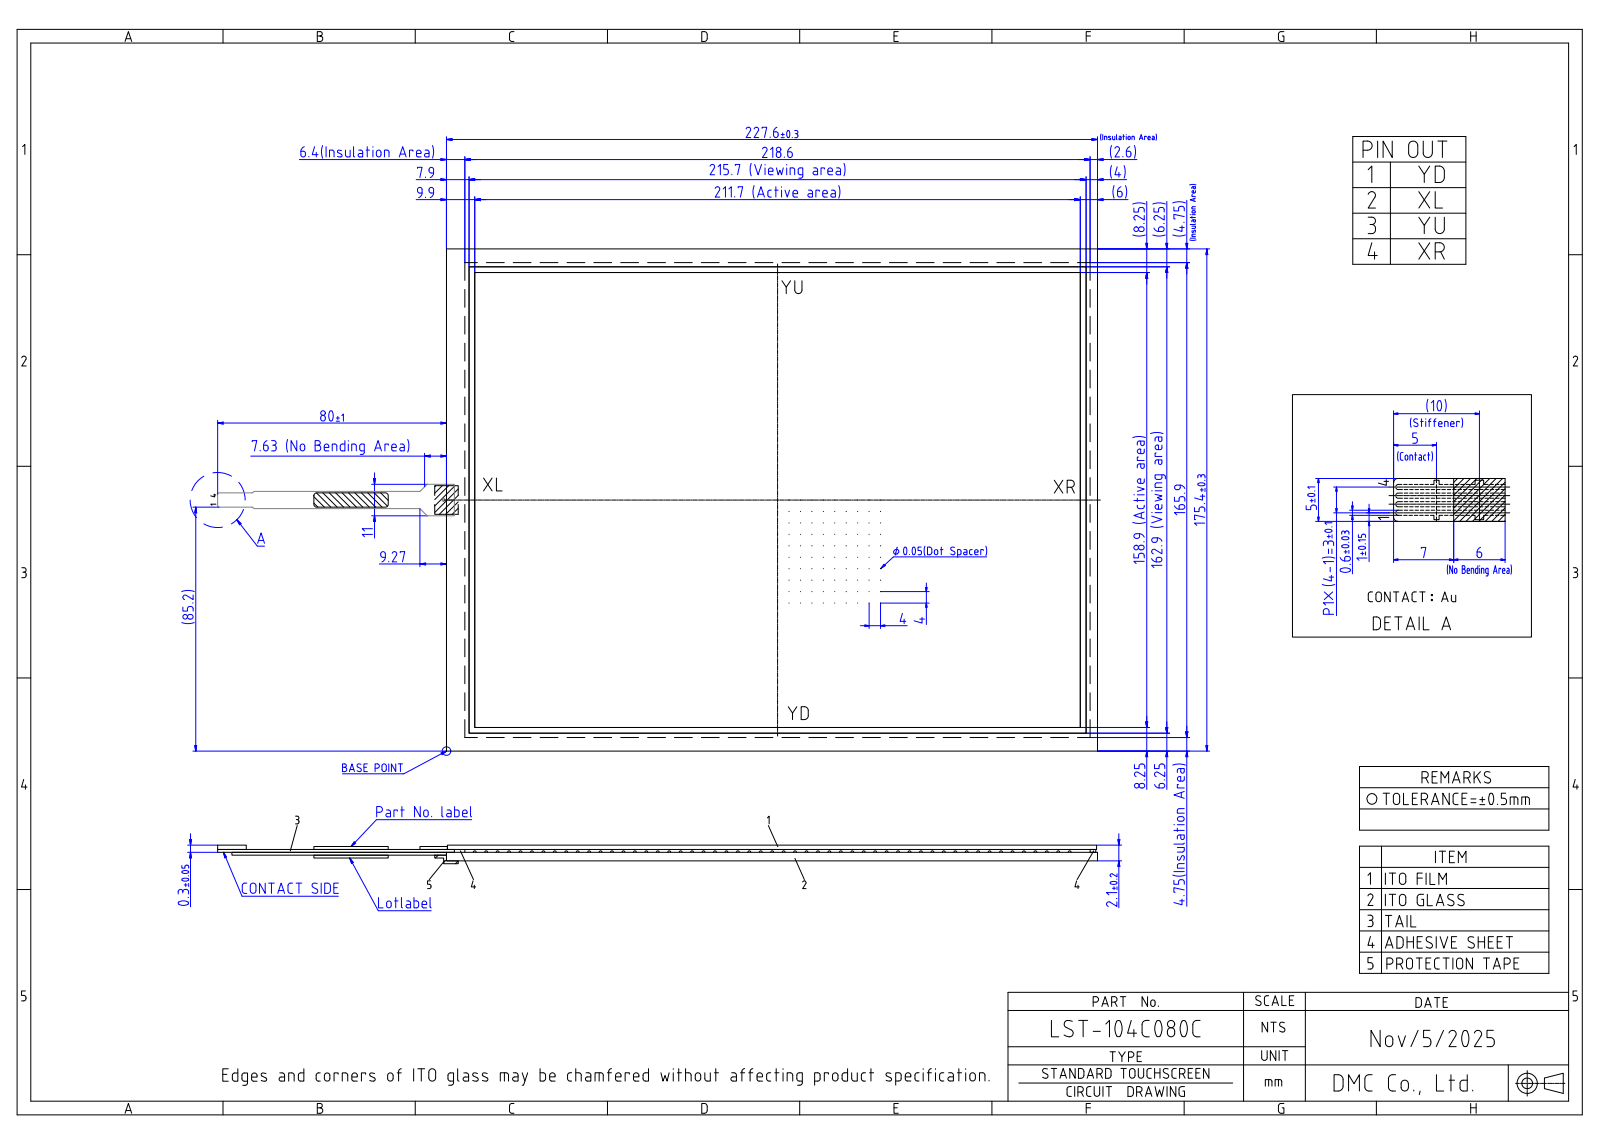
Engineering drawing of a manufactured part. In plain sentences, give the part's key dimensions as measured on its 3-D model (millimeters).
The part is named "LST-104C080C". Its 3-D file was written by "Autodesk Inventor 2020 (CONFIG_CONTROL_DESIGN)". It is 2 solids with 52 faces: 46 planar, 6 cylindrical and 0 other. Overall it measures 353.12 by 245.56 by 2.6 millimeters. Its volume is 83 747 cubic millimeters and its surface area 82 718 square millimeters. Partial cylindrical surfaces (rounded edges, fillets, slot ends): 4 of radius 0.3, 2 of radius 0.5. The main face-to-face distances are 2.1, 2, 2.2, 175.4, 2.3, 227.6, 0.5, 0.6, 0.4, 2.6.
